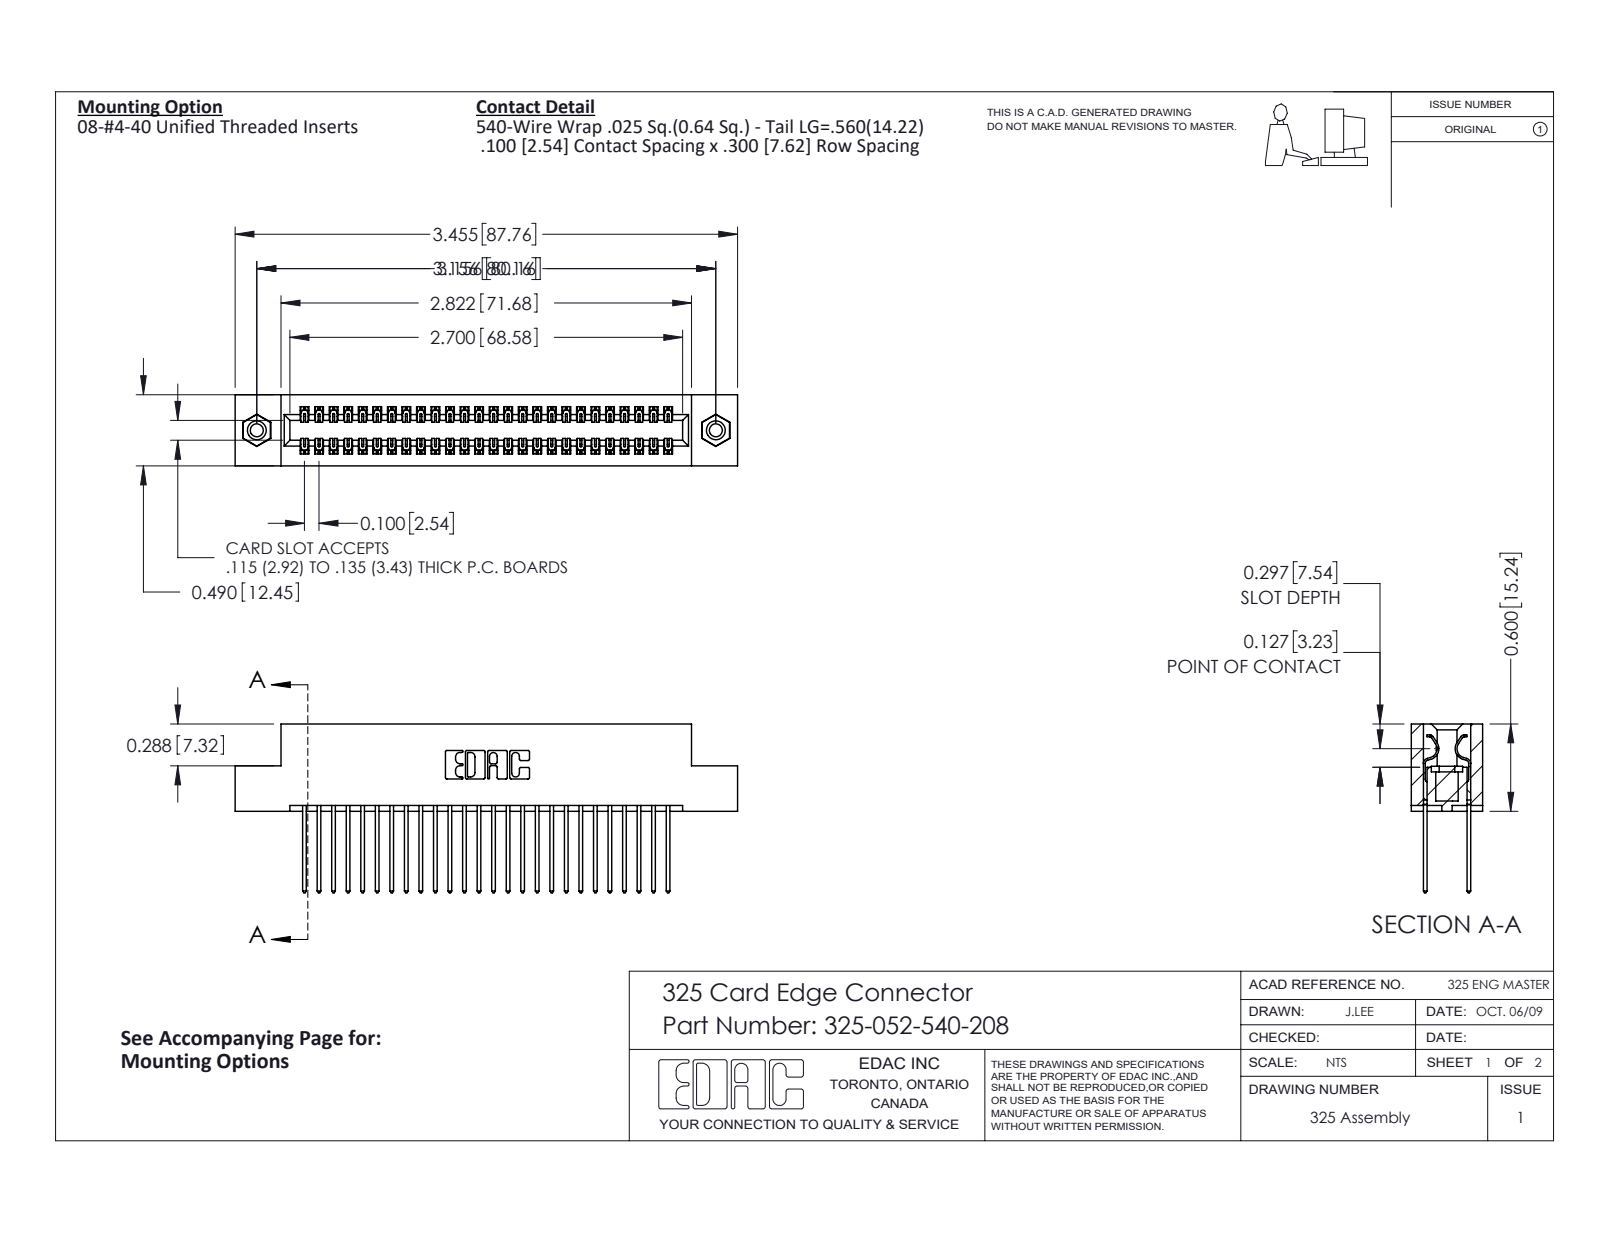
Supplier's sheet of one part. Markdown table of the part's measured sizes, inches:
| quantity | value |
| --- | --- |
| part name | 325-292-001_325-293-140; 325-052-540-208; 345-250-001_345-250-003-102; 325 Part_TI |
| STEP written by | SolidWorks 2016 (CONFIG_CONTROL_DESIGN) |
| units | inches |
| bodies | 55 solids, 2878 faces (1974 planar, 888 cylindrical, 16 other) |
| overall size | 3.455 × 1.16 × 0.49 |
| volume | 0.694 in³ |
| surface area | 22.23 in² |
| round holes (diameter × count) | 0.089 × 2, 0.125 × 2, 0.16 × 2 |
| round bosses / shafts (diameter × count) | 0.155 × 2 |
| partial cylindrical surfaces (radius × count) | 0.006 × 78, 0.01 × 52, 0.01 × 22, 0.007 × 6, 0.031 × 6, 0.026 × 3, 0.014 × 2, 0.022 × 2 |
| main face-to-face distances | 0.083, 0.407, 0.3, 0.107, 0.383, 0.025, 0.49, 0.325, 0.275, 0.04 |
| hole center spacings | 3.156 |
